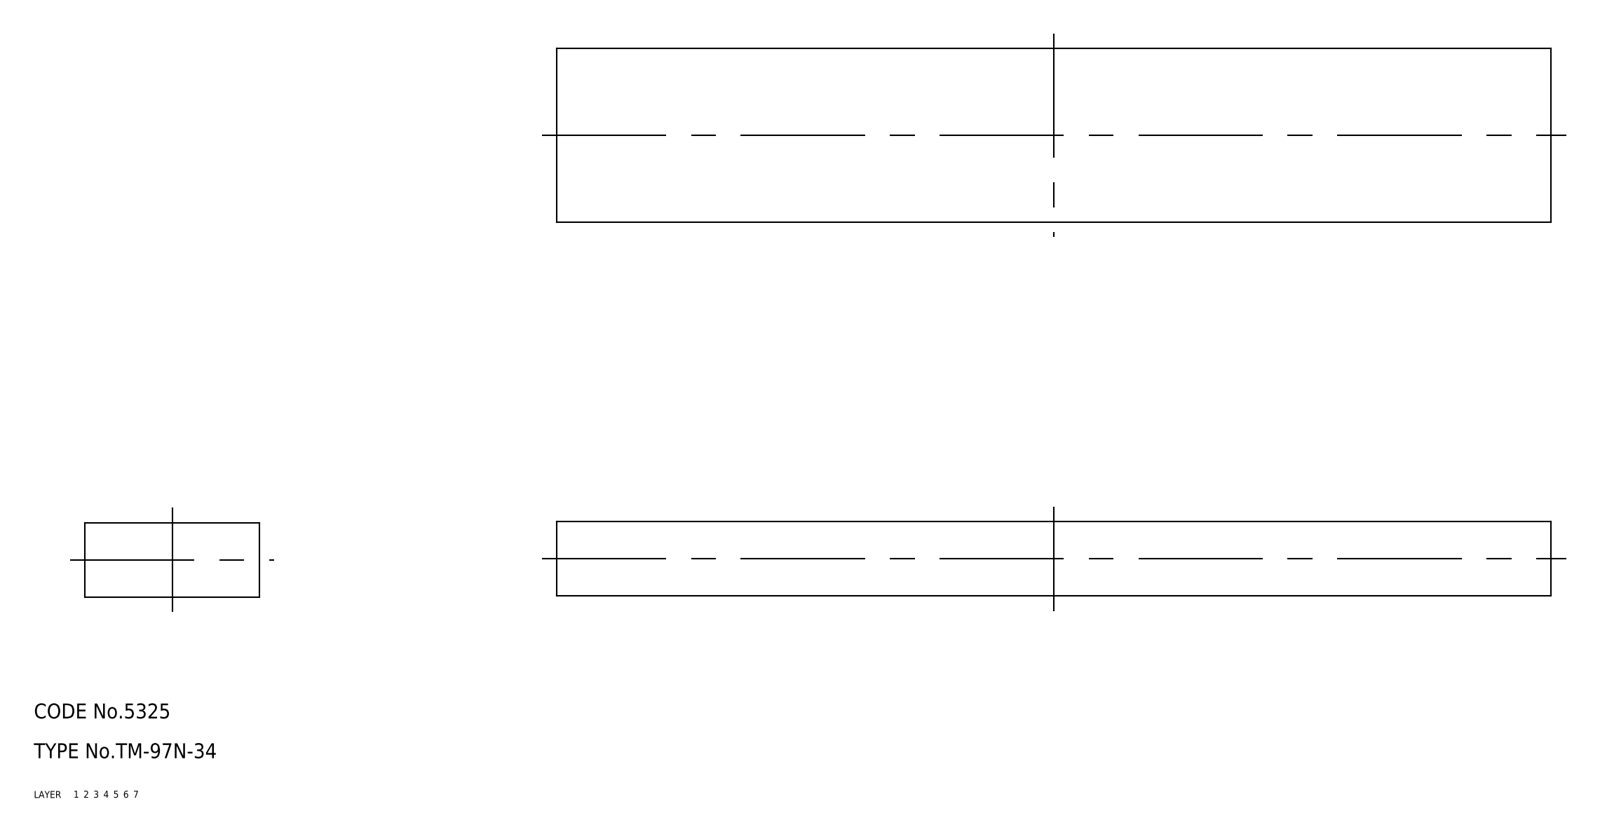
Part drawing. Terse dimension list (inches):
name: rubber foam
written by: CADfix (AUTOMOTIVE_DESIGN)
unit: in
bodies: 1 solid, 6 faces (0 planar, 0 cylindrical, 6 other)
size: 7.874 × 1.378 × 0.591
volume: 6.407 in³; area: 32.63 in²
